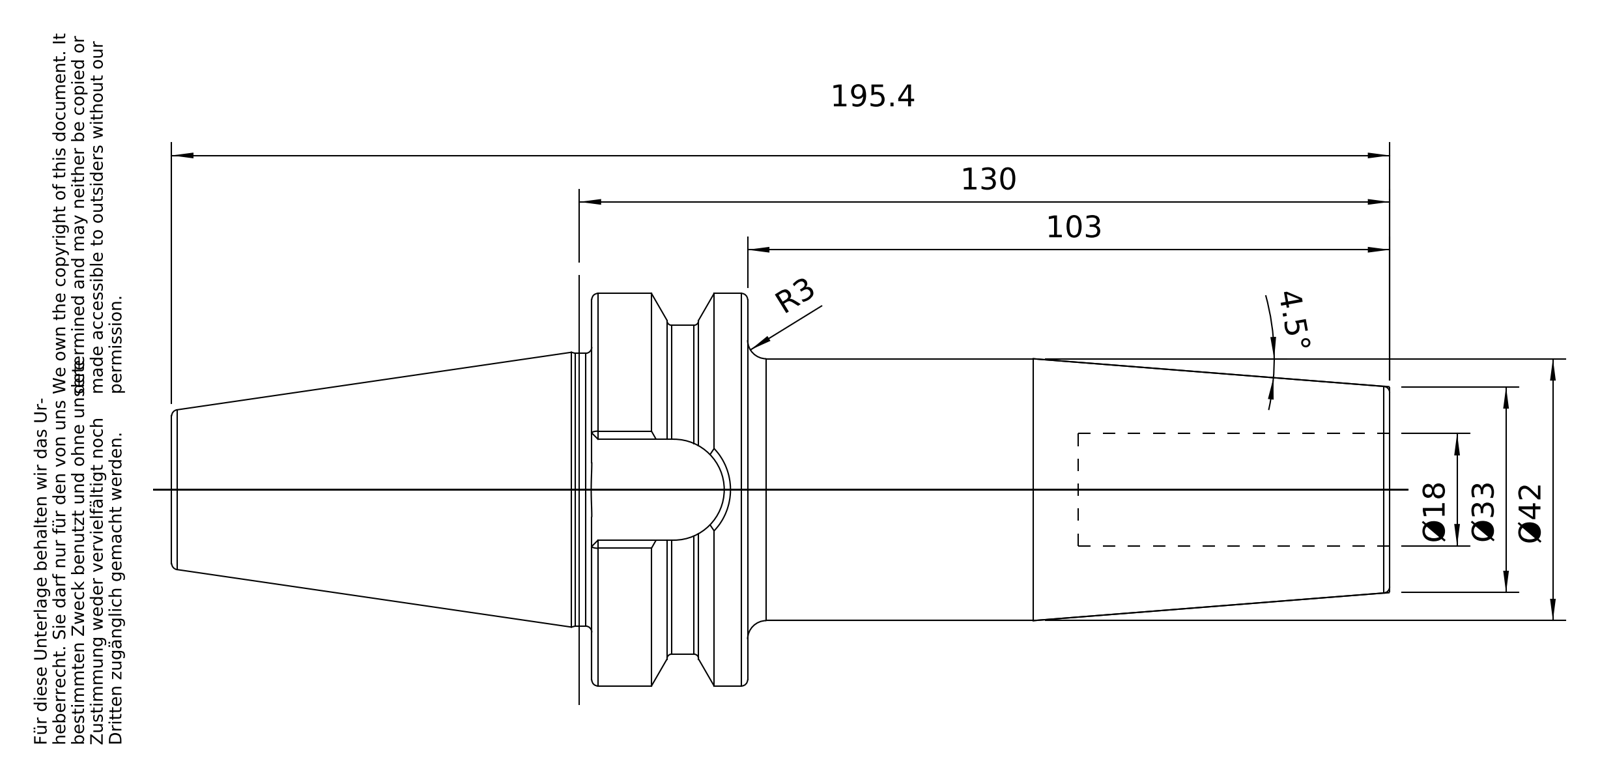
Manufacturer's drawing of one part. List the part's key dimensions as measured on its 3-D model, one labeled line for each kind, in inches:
Part name (STEP PRODUCT): 40-644-18
STEP written by: PRO/ENGINEER BY PARAMETRIC TECHNOLOGY CORPORATION, 2010430 (CONFIG_CONTROL_DESIGN)
Units: inches
Bodies: 1 solid, 96 faces (26 planar, 22 cylindrical, 48 other)
Overall size (bounding box): 7.693 × 2.48 × 2.48
Volume: 14.68 in³ · Surface area: 56.93 in²
Round holes (diameter × count): ⌀0.545 ×1, ⌀0.67 ×1, ⌀0.689 ×1, ⌀0.709 ×1
Round bosses / shafts (diameter × count): ⌀2.48 ×1, ⌀2.077 ×1, ⌀1.722 ×1, ⌀1.654 ×1, ⌀0.63 ×1
Partial cylindrical surfaces — rounded edges, fillets, slot ends (radius × count): R0.319 ×1
Main face-to-face distances: 0.984, 5.039, 4.055, 1.768, 3.071, 2.087, 1.969, 0.638, 2.654, 3.638
